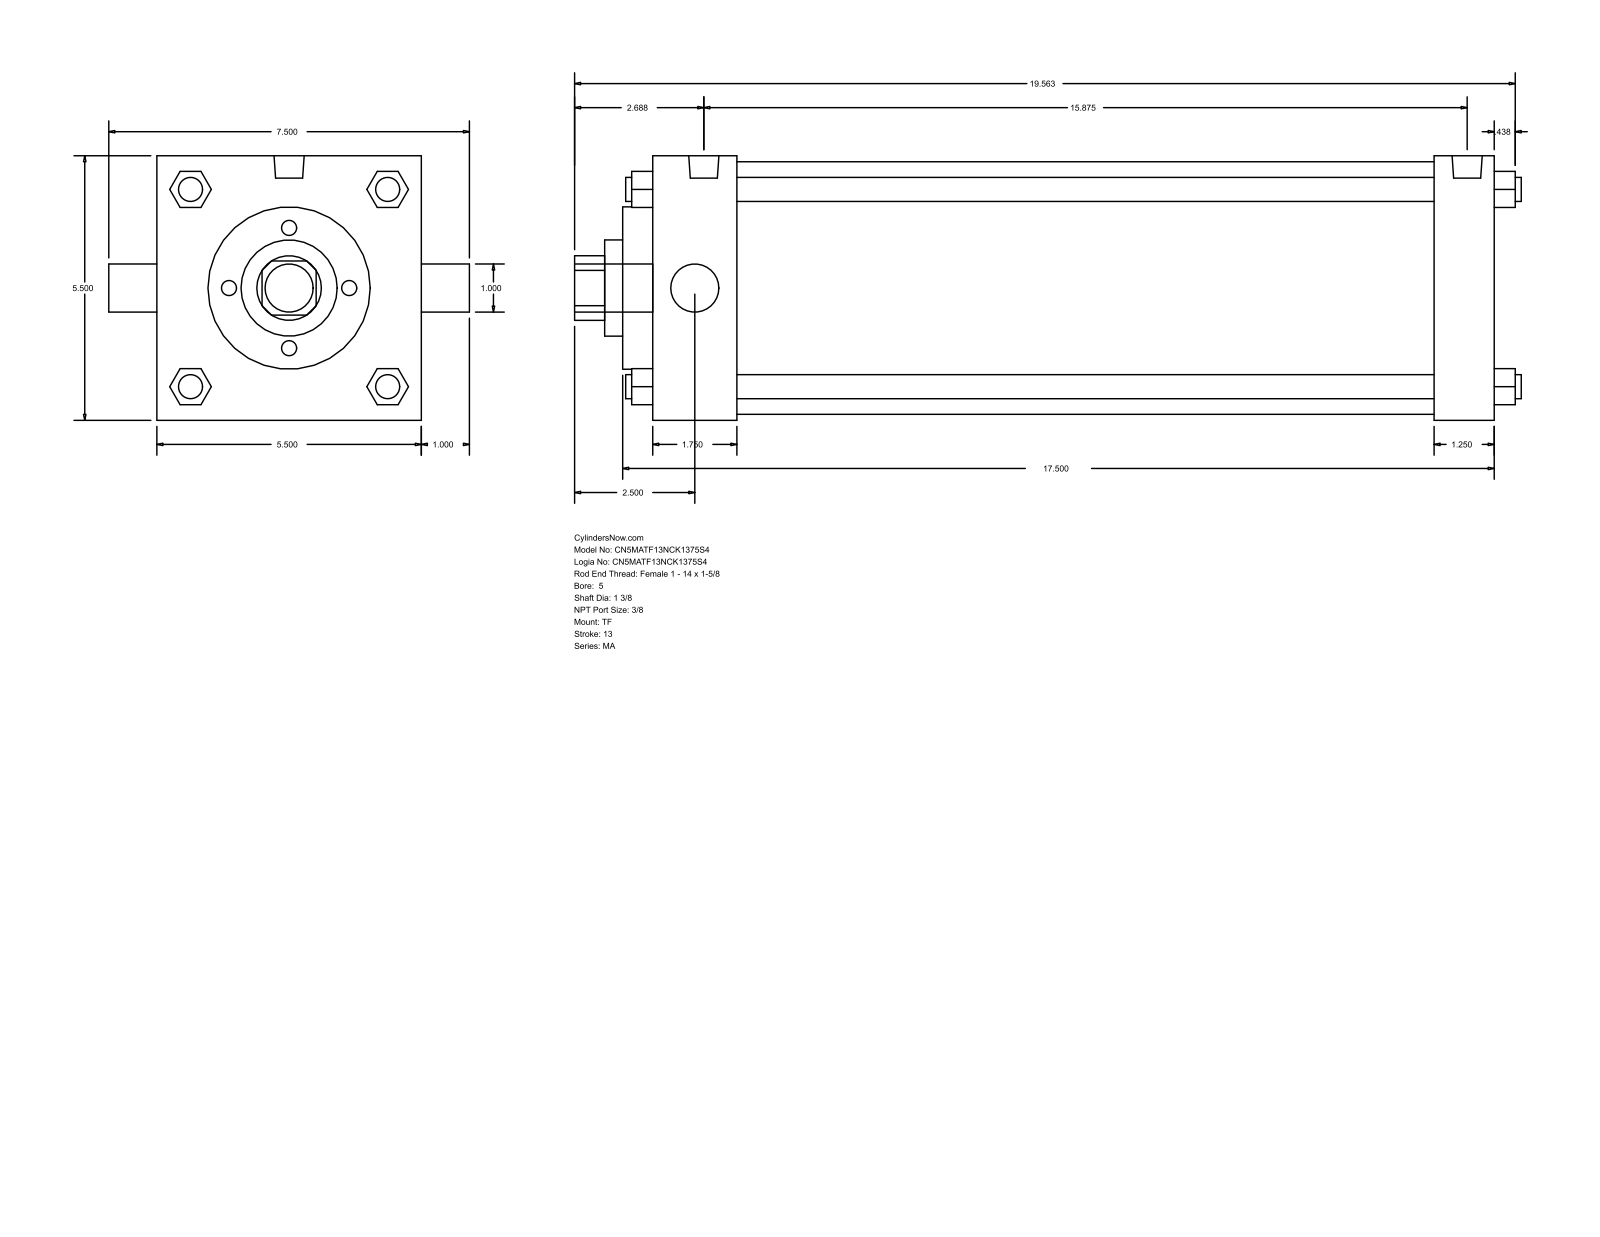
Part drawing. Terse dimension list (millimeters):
name: MA_TF__0500_1.375
written by: GSSL Pune (CONFIG_CONTROL_DESIGN)
unit: mm
bodies: 0 solids, 122 faces (93 planar, 29 cylindrical, 0 other)
size: 500.06 × 190.5 × 139.7
holes: 1× ⌀25.4, 1× ⌀34.92, 1× ⌀50.8, 1× ⌀85.72, 1× ⌀133.35
bosses: 4× ⌀12.7, 3× ⌀11.11, 2× ⌀15.93, 1× ⌀25.4
rounds: 1× R17.06
face distances: 139.7, 444.5, 412.75, 31.75, 44.45, 368.3, 400.05, 15.87, 60.32, 428.62
